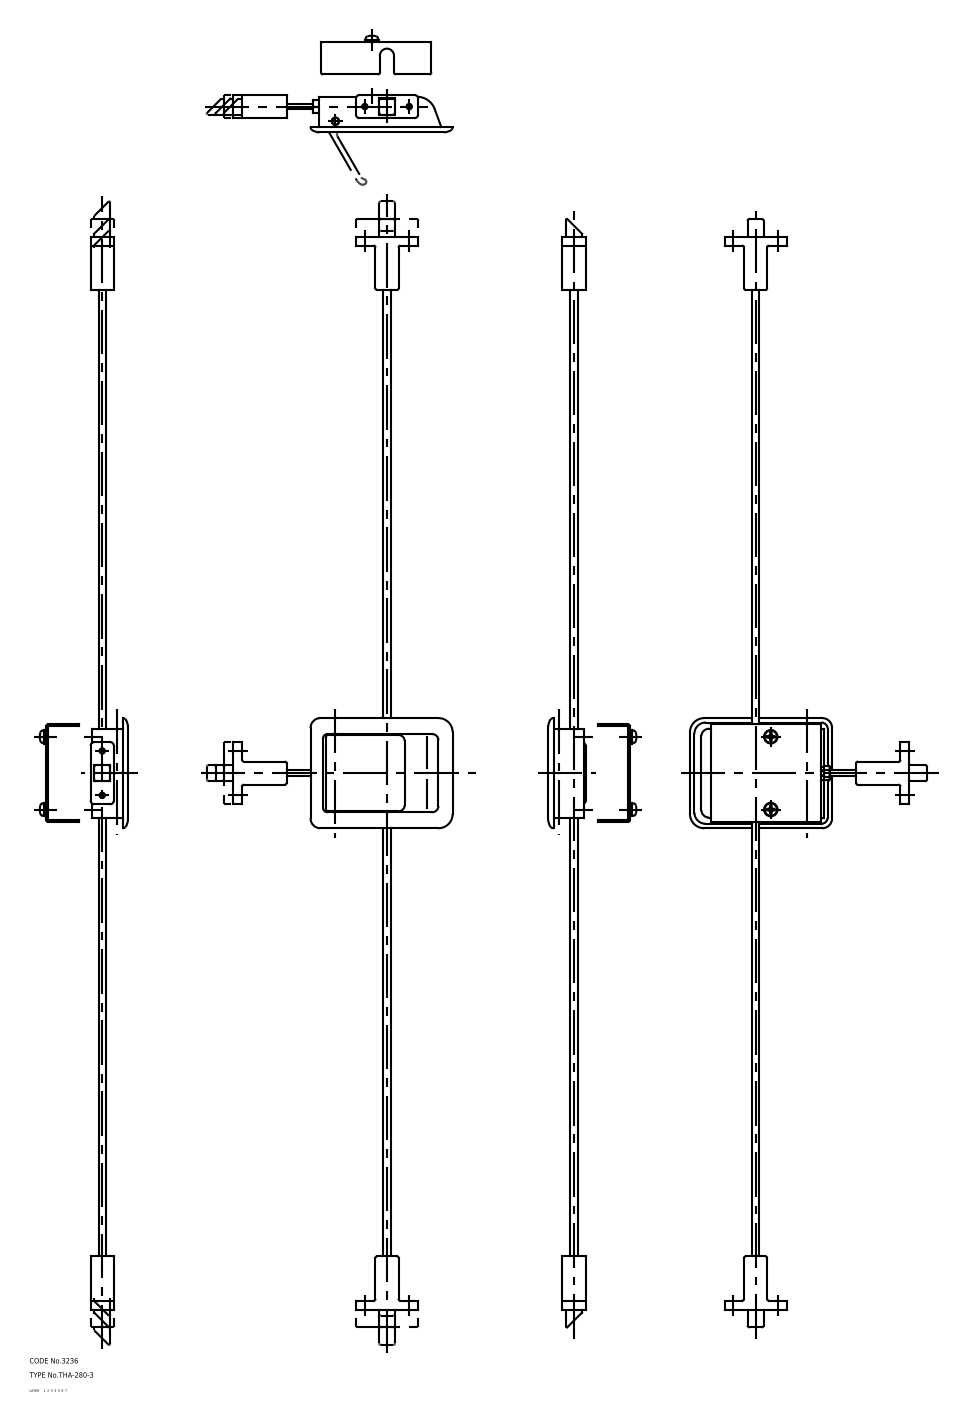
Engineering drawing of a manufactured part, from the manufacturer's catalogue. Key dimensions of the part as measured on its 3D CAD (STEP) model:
Part name (STEP PRODUCT): latch; case; screw; shaft (+8 more)
STEP written by: CADfix (AUTOMOTIVE_DESIGN)
Units: millimetres
Bodies: 17 solids, 468 faces (0 planar, 0 cylindrical, 468 other)
Overall size (bounding box): 624 × 133.5 × 27.05
Volume: 74 799 mm³ · Surface area: 60 626 mm²
